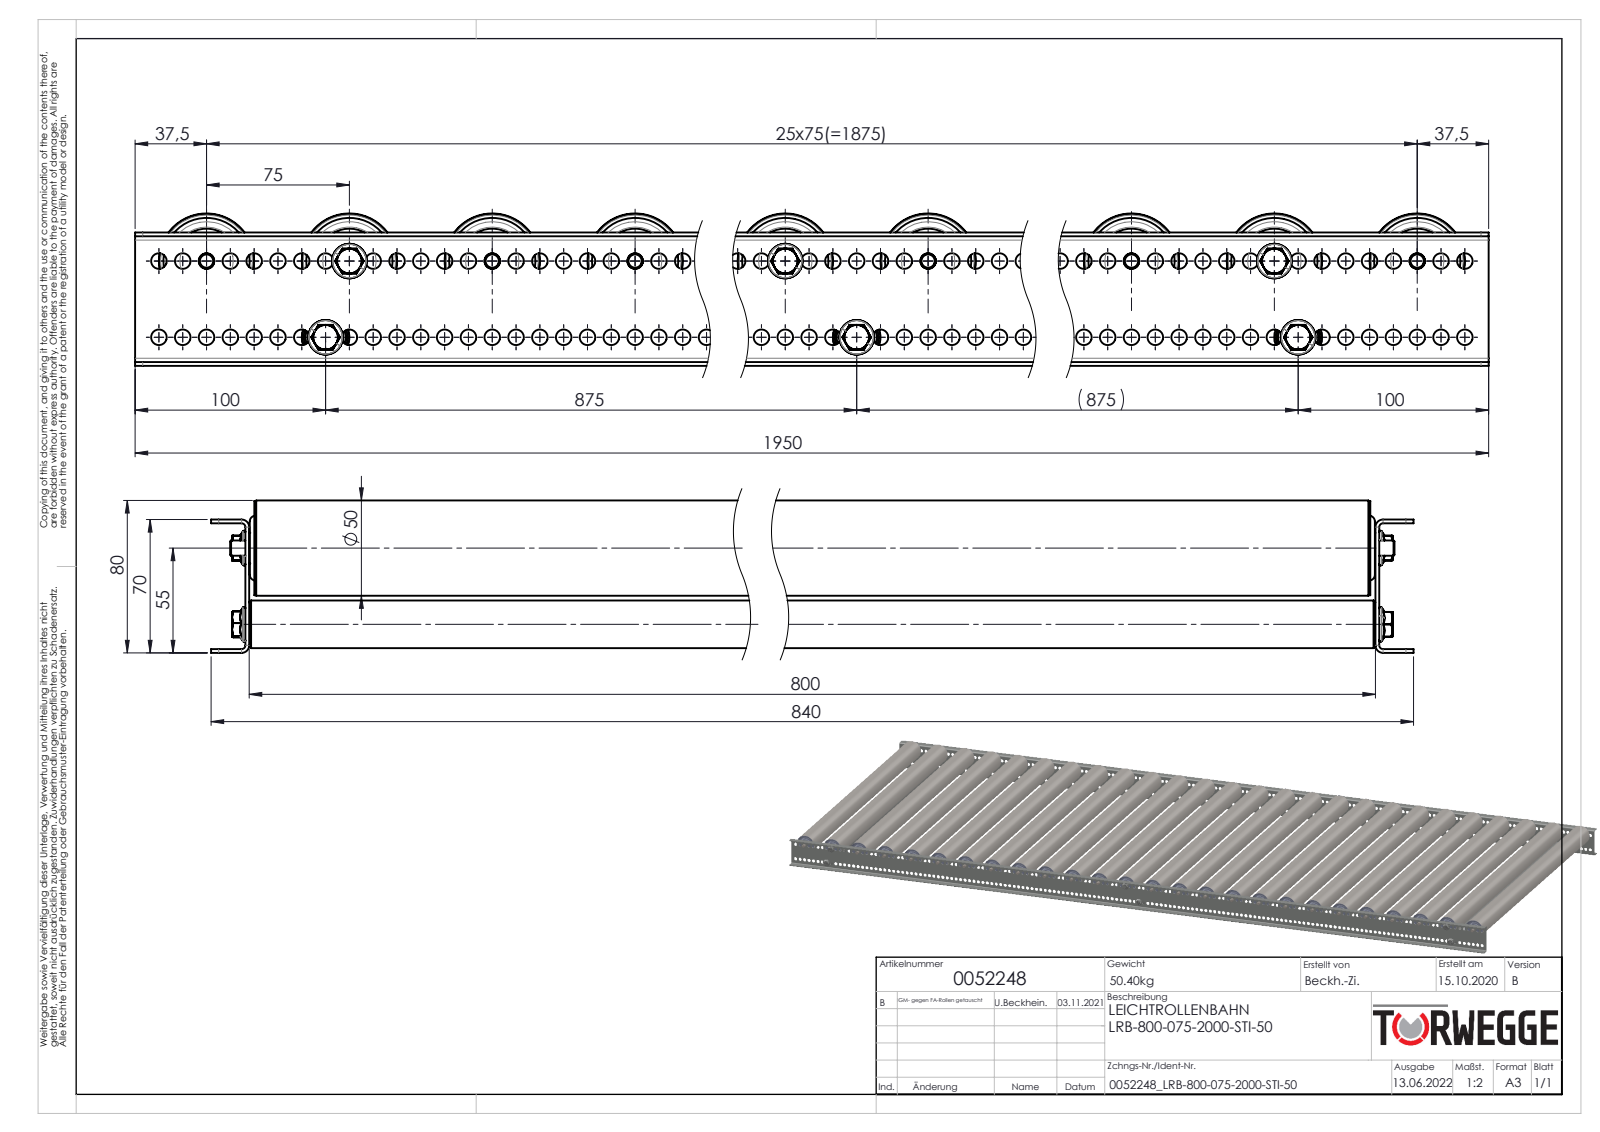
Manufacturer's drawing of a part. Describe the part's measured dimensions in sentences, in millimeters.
The part is named "Traversen_KFG_L800; S100994_Sperrzahnschraube_M08x16-8.8-A2K; 0039771_Tragrollenrohr-Ø50x1,5STI_KFG_EL800; Druckfeder_1,2x10x30 (+8 more)". Its 3-D file was written by "SolidWorks 2020 (AUTOMOTIVE_DESIGN)". It is 602 solids with 10646 faces: 2112 planar, 3872 cylindrical and 4662 other. Overall it measures 1950 by 840 by 80 millimeters. Its volume is 7 519 000 cubic millimeters and its surface area 8 758 000 square millimeters. Round holes: 310 of diameter 8.2, 26 of diameter 17.1, 26 of diameter 18.5, 26 of diameter 27.7, 26 of diameter 45.3, 26 of diameter 47, 23 of diameter 7.6, 6 of diameter 6.8, 3 of diameter 12, 3 of diameter 12.2, 3 of diameter 19.2, 3 of diameter 21. Round bosses or shafts: 29 of diameter 8, 26 of diameter 50, 26 of diameter 49.5, 26 of diameter 47.3, 26 of diameter 29.7, 26 of diameter 27.4, 26 of diameter 27.3, 26 of diameter 16. Partial cylindrical surfaces (rounded edges, fillets, slot ends): 46 of radius 0.6, 46 of radius 0.75, 46 of radius 2.45, 23 of radius 4.87, 23 of radius 7, 12 of radius 2.5, 8 of radius 4, 4 of radius 2. The main face-to-face distances are 2, 802, 68, 800, 804, 70, 66, 1, 2.3, 801.7. The hole center spacings are 12.5, 25, 37.5, 50, 62.5, 75, 87.5, 100.
